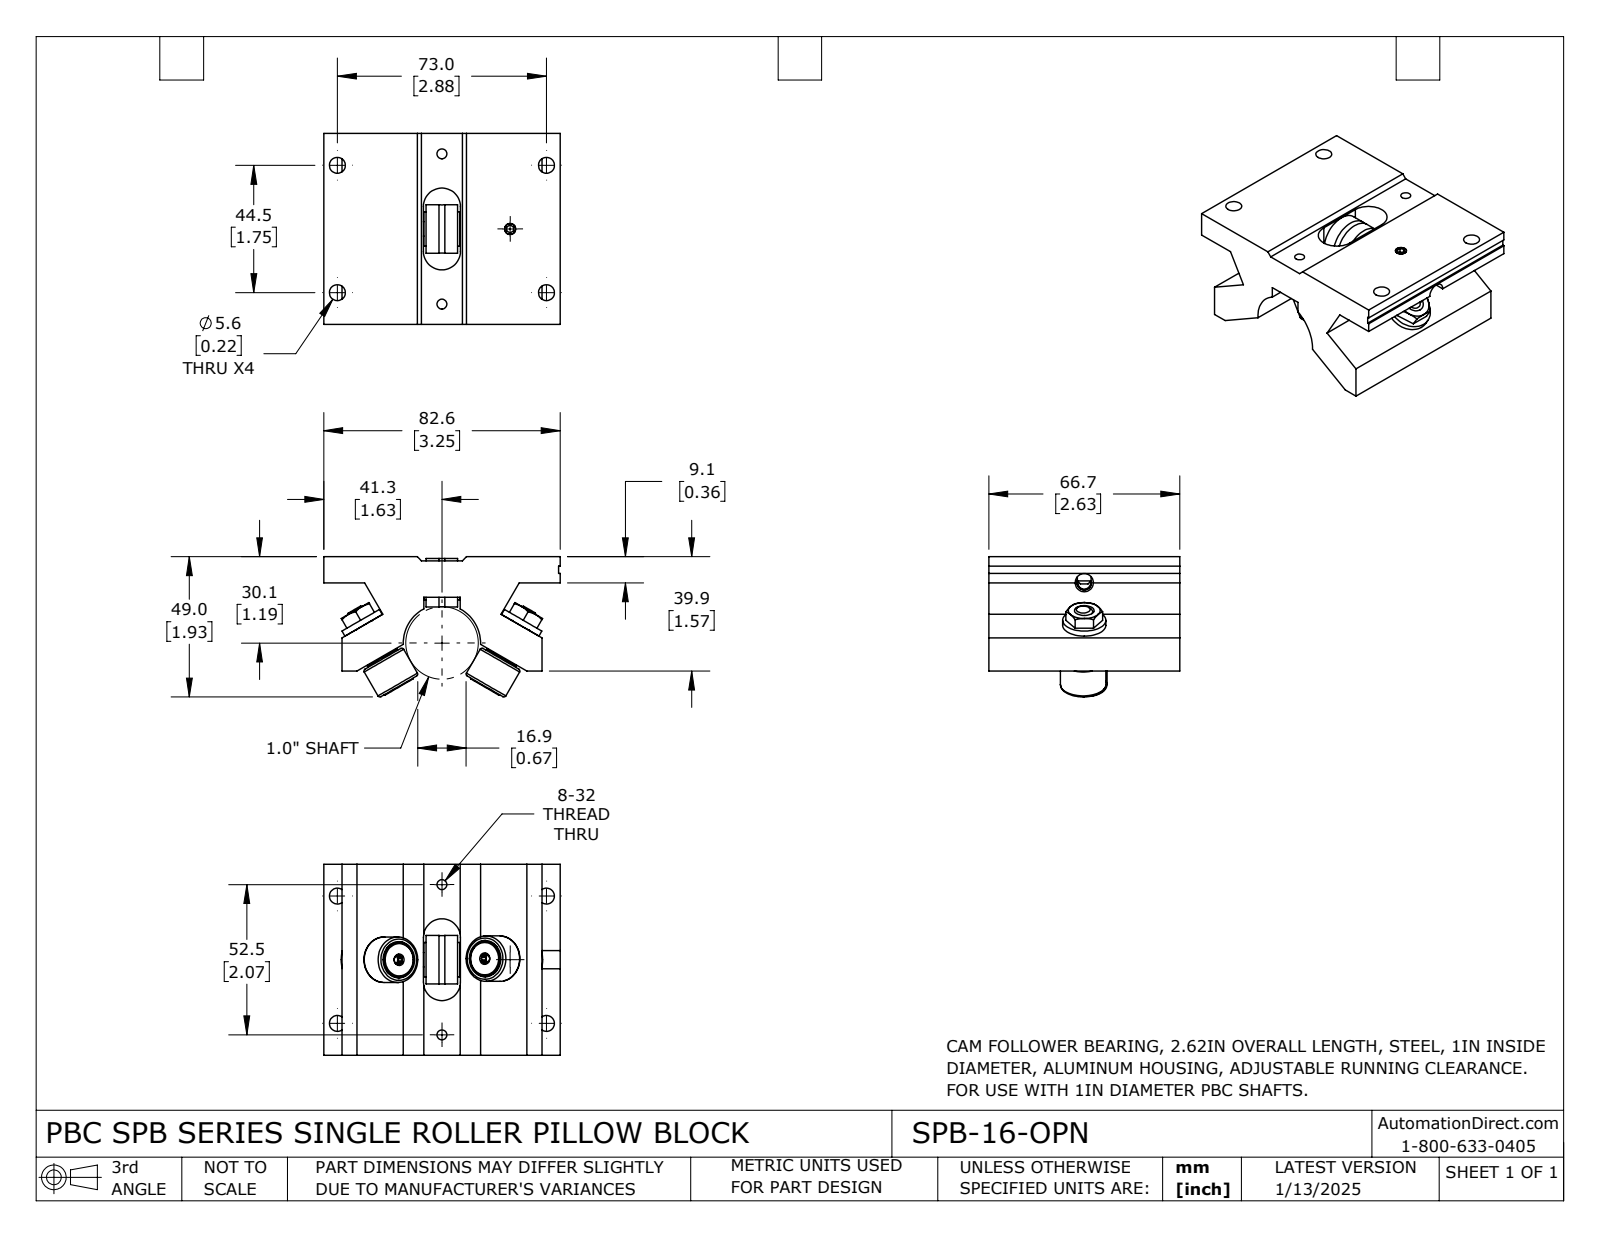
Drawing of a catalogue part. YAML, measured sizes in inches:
part_name: "SPB-16-OPN"
step_written_by: "SolidWorks 2023 (CONFIG_CONTROL_DESIGN)"
units: inches
bodies: {solids: 8, faces: 281, planar: 119, cylindrical: 88, other: 74}
overall_size: [3.25, 2.625, 1.928]
volume: 7.436
surface_area: 50.95
round_holes:
  - {diameter: 0.219, count: 4}
  - {diameter: 0.129, count: 2}
  - {diameter: 0.136, count: 2}
  - {diameter: 0.204, count: 2}
  - {diameter: 0.499, count: 2}
  - {diameter: 0.15, count: 1}
  - {diameter: 0.156, count: 1}
  - {diameter: 0.197, count: 1}
  - {diameter: 0.25, count: 1}
  - {diameter: 0.253, count: 1}
  - {diameter: 0.26, count: 1}
  - {diameter: 0.377, count: 1}
round_bosses_or_shafts:
  - {diameter: 0.625, count: 2}
  - {diameter: 0.594, count: 2}
  - {diameter: 0.469, count: 2}
  - {diameter: 0.666, count: 1}
  - {diameter: 0.472, count: 1}
  - {diameter: 0.405, count: 1}
  - {diameter: 0.26, count: 1}
  - {diameter: 0.255, count: 1}
partial_cylinders:
  - {radius: 0.255, count: 2}
  - {radius: 0.531, count: 1}
face_to_face_distances: [0.5, 2.625, 0.36, 0.25, 3, 2.75, 1.212, 1.572, 1.515, 0.303]
hole_center_spacings: [1.446, 2.389, 1.395, 2.531, 2.875, 3.366, 0.015, 1.007]
